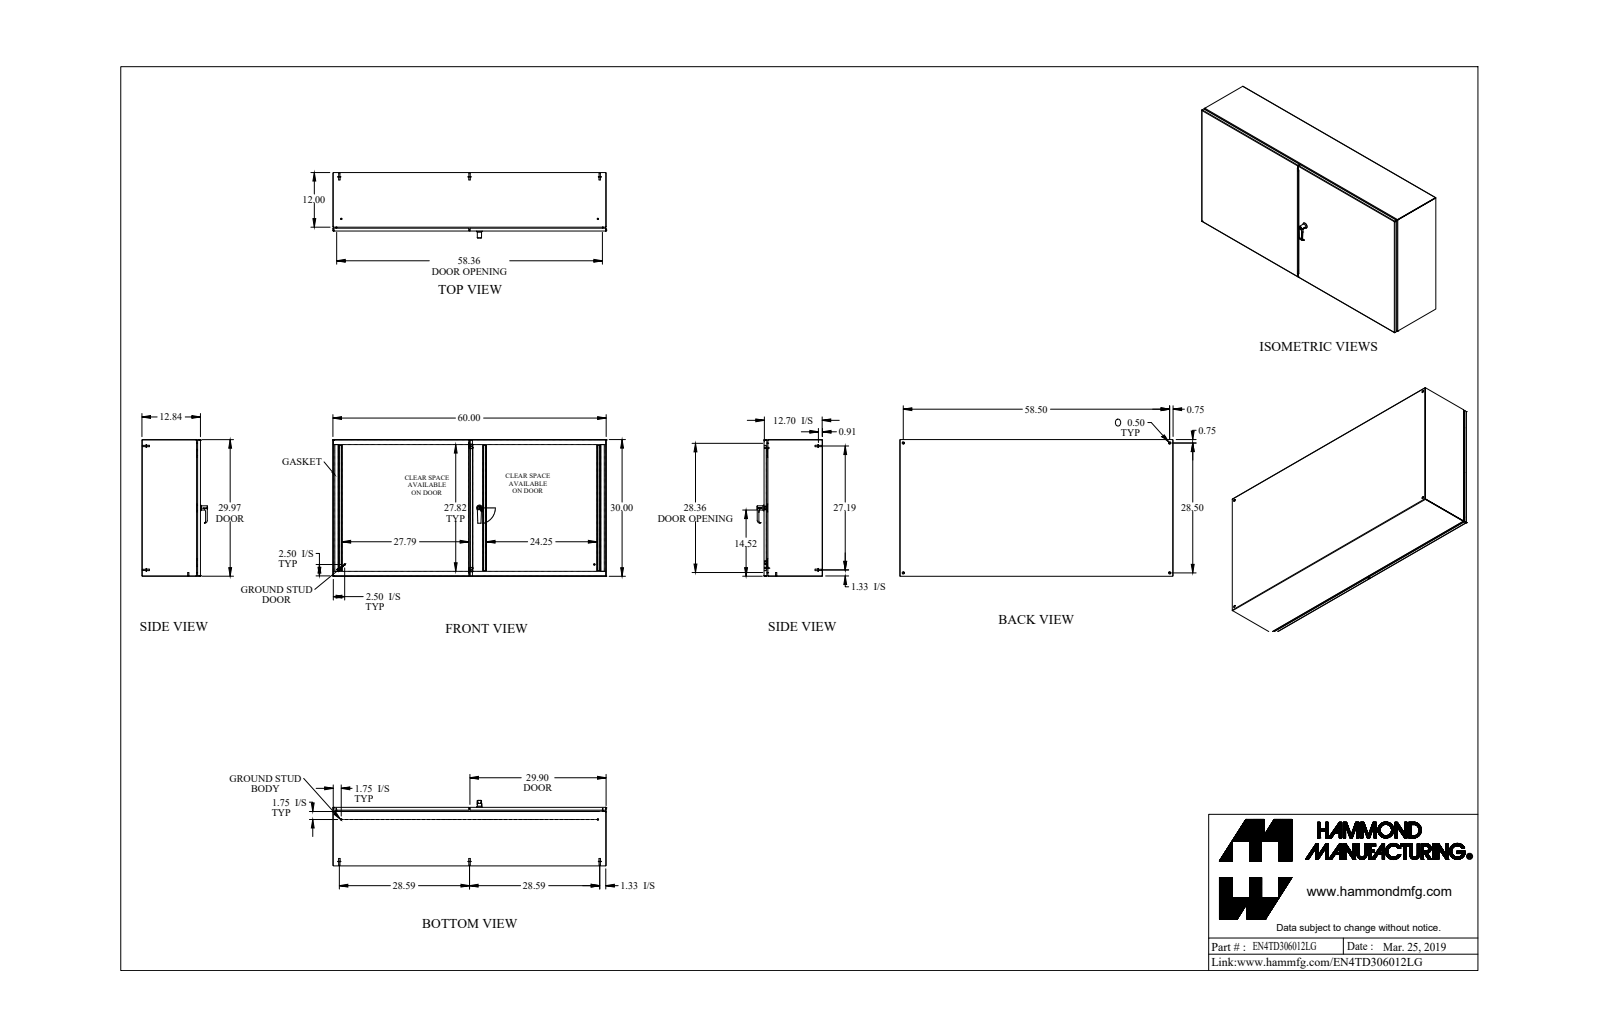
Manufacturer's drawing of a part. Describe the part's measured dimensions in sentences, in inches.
The part is named "EN4TD306012LG". Its 3-D file was written by "SolidWorks 2018 (AUTOMOTIVE_DESIGN)". It is 91 solids with 2297 faces: 1053 planar, 846 cylindrical and 398 other. Overall it measures 60 by 30 by 14.372 inches. Its volume is 510.1 cubic inches and its surface area 13 647 square inches. Round holes: 5 of diameter 0.196, 4 of diameter 0.176, 4 of diameter 0.265, 4 of diameter 0.5, 3 of diameter 0.24, 3 of diameter 0.242, 2 of diameter 0.172, 2 of diameter 0.25, 2 of diameter 0.256, 2 of diameter 0.26, 2 of diameter 0.275, 2 of diameter 0.313. Round bosses or shafts: 10 of diameter 0.25, 8 of diameter 0.625, 6 of diameter 0.313, 6 of diameter 0.27, 4 of diameter 0.51, 4 of diameter 0.281, 4 of diameter 0.156, 3 of diameter 0.75. Partial cylindrical surfaces (rounded edges, fillets, slot ends): 30 of radius 0.043, 30 of radius 0.081, 26 of radius 0.036, 26 of radius 0.108, 25 of radius 0.063, 20 of radius 0.094, 16 of radius 0.02, 15 of radius 0.016. The main face-to-face distances are 0.072, 12.77, 12.698, 12.842, 29.928, 29.856, 59.928, 30, 59.856, 60. The hole center spacings are 0.786, 13.188, 26.792, 28.5, 30.603, 31.748, 34.498, 58.5.
